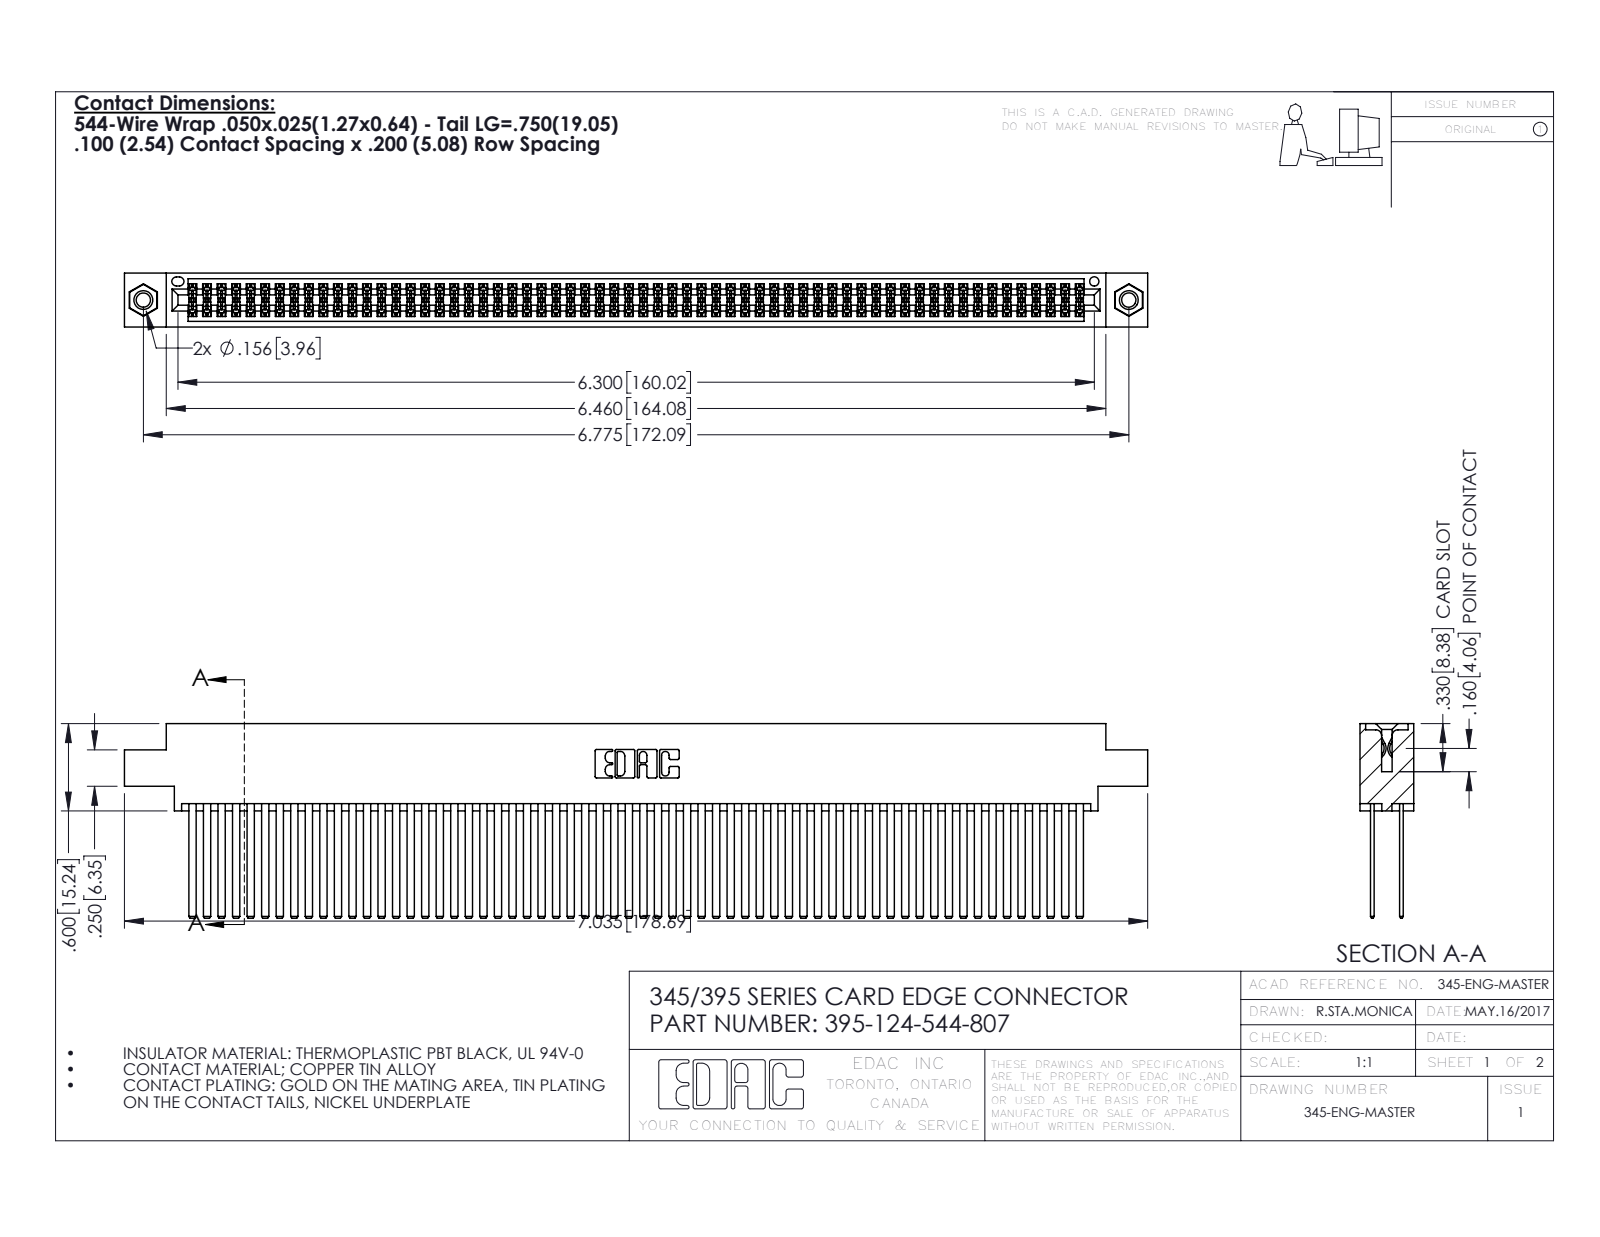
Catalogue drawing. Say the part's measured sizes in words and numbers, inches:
The part is named "345-292-001_345-293-144; 345-250-001_345-250-005-103; 345 Part_0.170 Offset - 0.156 Dia-TI; 395-124-544-807". Its 3-D file was written by "SolidWorks 2016 (CONFIG_CONTROL_DESIGN)". It is 127 solids with 5646 faces: 3712 planar, 1918 cylindrical and 16 other. Overall it measures 7.035 by 1.337 by 0.37 inches. Its volume is 1.169 cubic inches and its surface area 52.65 square inches. Round holes: 2 of diameter 0.098, 2 of diameter 0.125, 2 of diameter 0.156, 1 of diameter 0.064. Round bosses or shafts: 2 of diameter 0.155. Partial cylindrical surfaces (rounded edges, fillets, slot ends): 186 of radius 0.006, 22 of radius 0.01, 6 of radius 0.007, 6 of radius 0.031, 3 of radius 0.026, 2 of radius 0.014, 2 of radius 0.019, 2 of radius 0.022. The main face-to-face distances are 0.2, 0.025, 0.072, 0.098, 0.272, 0.298, 0.225, 0.175, 0.37, 0.15. The hole center spacings are 0.27, 6.539, 6.775.
